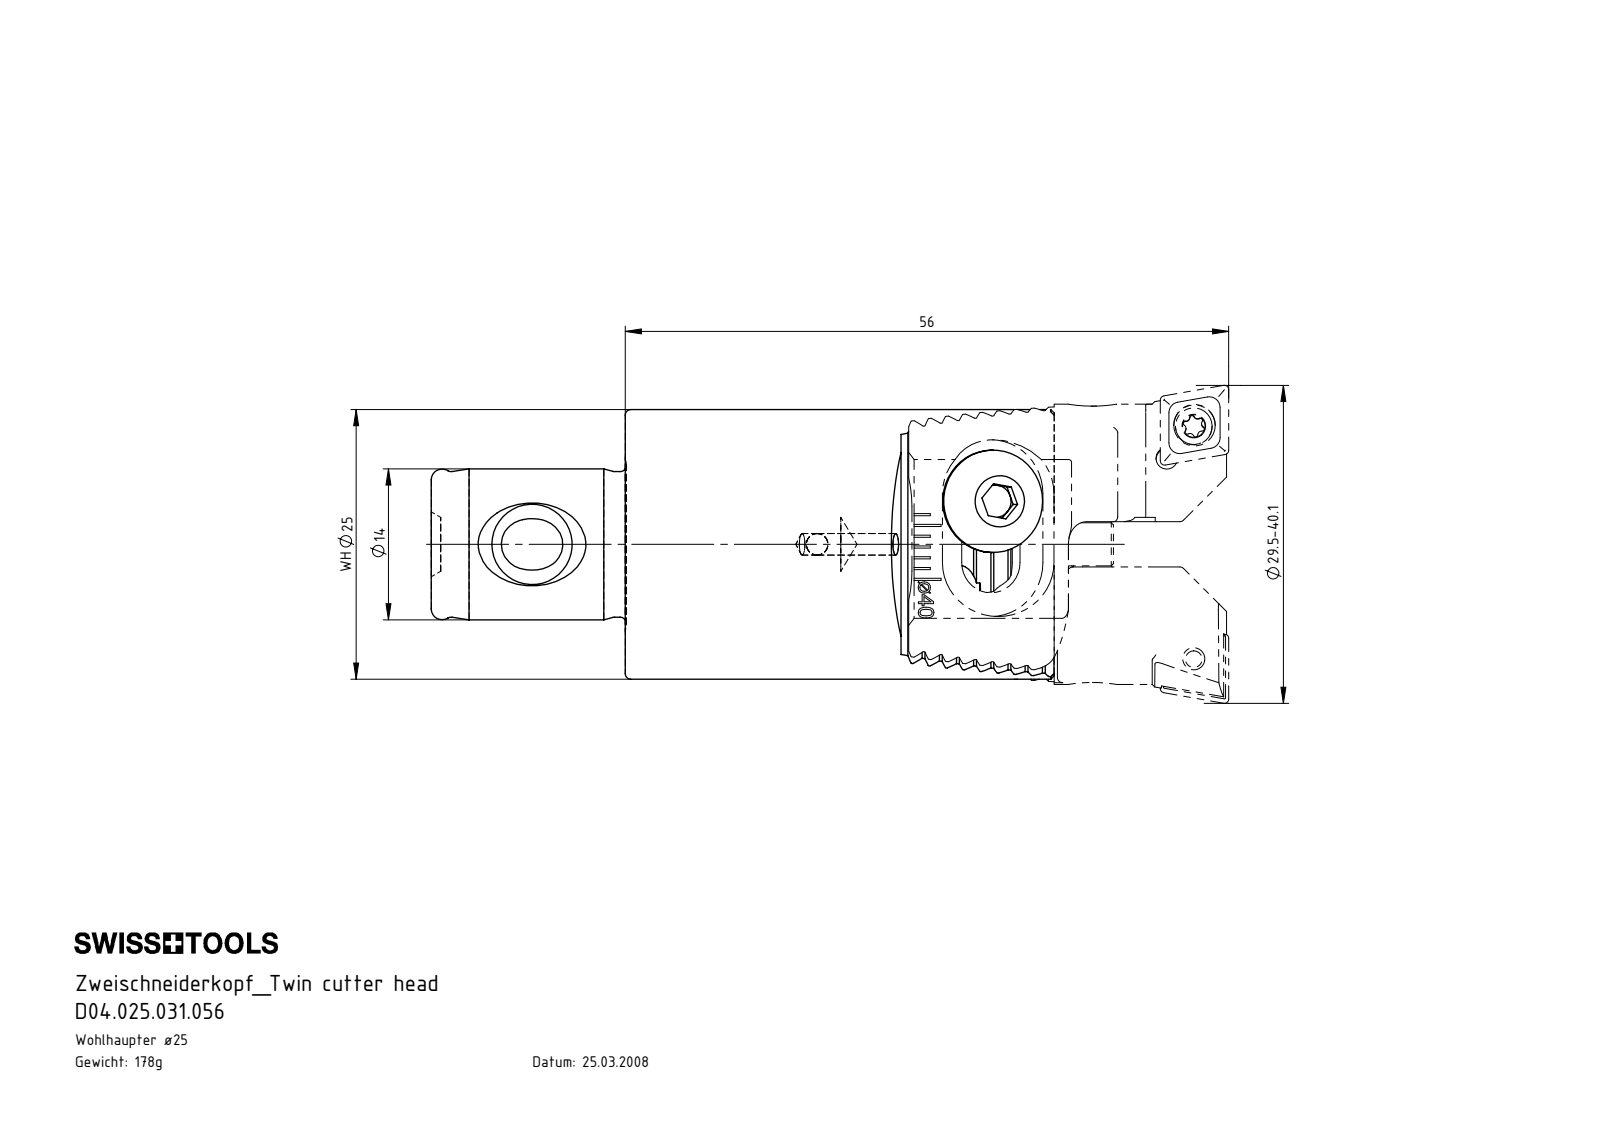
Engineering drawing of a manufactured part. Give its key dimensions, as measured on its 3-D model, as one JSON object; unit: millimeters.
{"part_name": "Z25-ER1.002.012_A; Z25-ER1.003.012_A_gespannt; D04.025.031.056; Z25-ER1.001.012 (+2 more)", "step_written_by": "SolidWorks 2015 (AUTOMOTIVE_DESIGN)", "units": "millimeters", "bodies": {"solids": 6, "faces": 323, "planar": 167, "cylindrical": 84, "other": 72}, "overall_size": [63.3, 25, 25], "volume_mm3": 17931, "surface_area_mm2": 7172, "round_holes": [[2.5, 4], [4.2, 2], [5.3, 2], [6, 2], [5, 1]], "round_bosses_or_shafts": [[9.5, 2], [9.2, 2], [5, 2], [25, 1], [14, 1], [13.5, 1], [4, 1], [3, 1]], "partial_cylinders_radius": [[0.12, 18], [220, 2]], "face_to_face_distances": [1.43, 2.86, 4.29, 5.72, 7.15, 5.71, 8.58, 7.14, 4.28, 8.57]}
